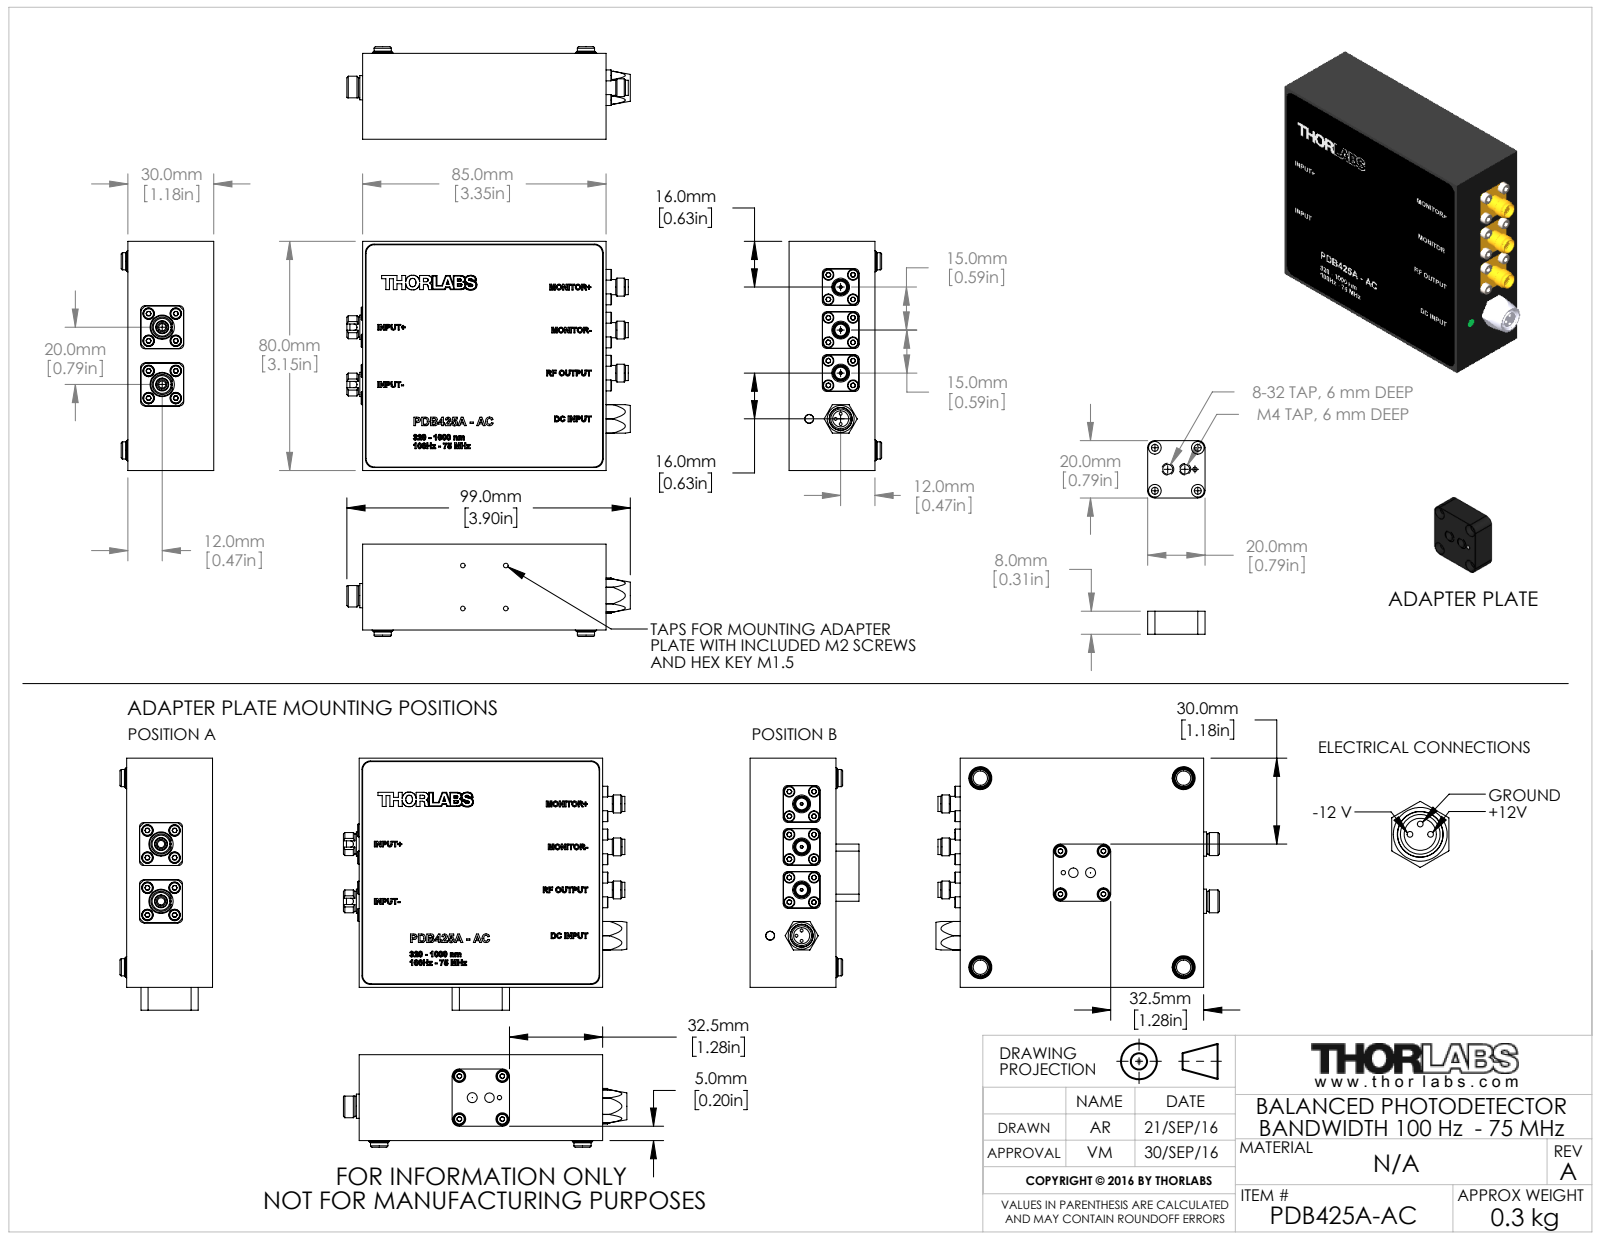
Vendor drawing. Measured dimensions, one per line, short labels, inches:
name: MTN005466-E0W
written by: SolidWorks 2014 (AUTOMOTIVE_DESIGN)
unit: in
bodies: 90 solids, 3084 faces (1802 planar, 584 cylindrical, 698 other)
size: 3.898 × 3.465 × 1.496
volume: 5.353 in³; area: 89.6 in²
holes: 38× ⌀0.063, 12× ⌀0.102, 8× ⌀0.087, 8× ⌀0.094, 8× ⌀0.157, 8× ⌀0.173, 6× ⌀0.04, 5× ⌀0.315, 3× ⌀0.031, 3× ⌀0.039, 3× ⌀0.161, 3× ⌀0.165
bosses: 20× ⌀0.15, 20× ⌀0.079, 8× ⌀0.177, 8× ⌀0.098, 6× ⌀0.017, 4× ⌀0.236, 3× ⌀0.245, 3× ⌀0.209
rounds: 20× R0.059, 12× R0.118, 8× R0.098, 8× R0.197, 4× R0.039, 2× R0.374, 1× R0.226
face distances: 1.169, 0.236, 0.933, 0.217, 3.15, 0.079, 2.933, 3.346, 0.138, 3.268
hole spacings: 0.591, 0.239, 0.339, 0.374, 0.265, 0.344, 0.454, 0.508
